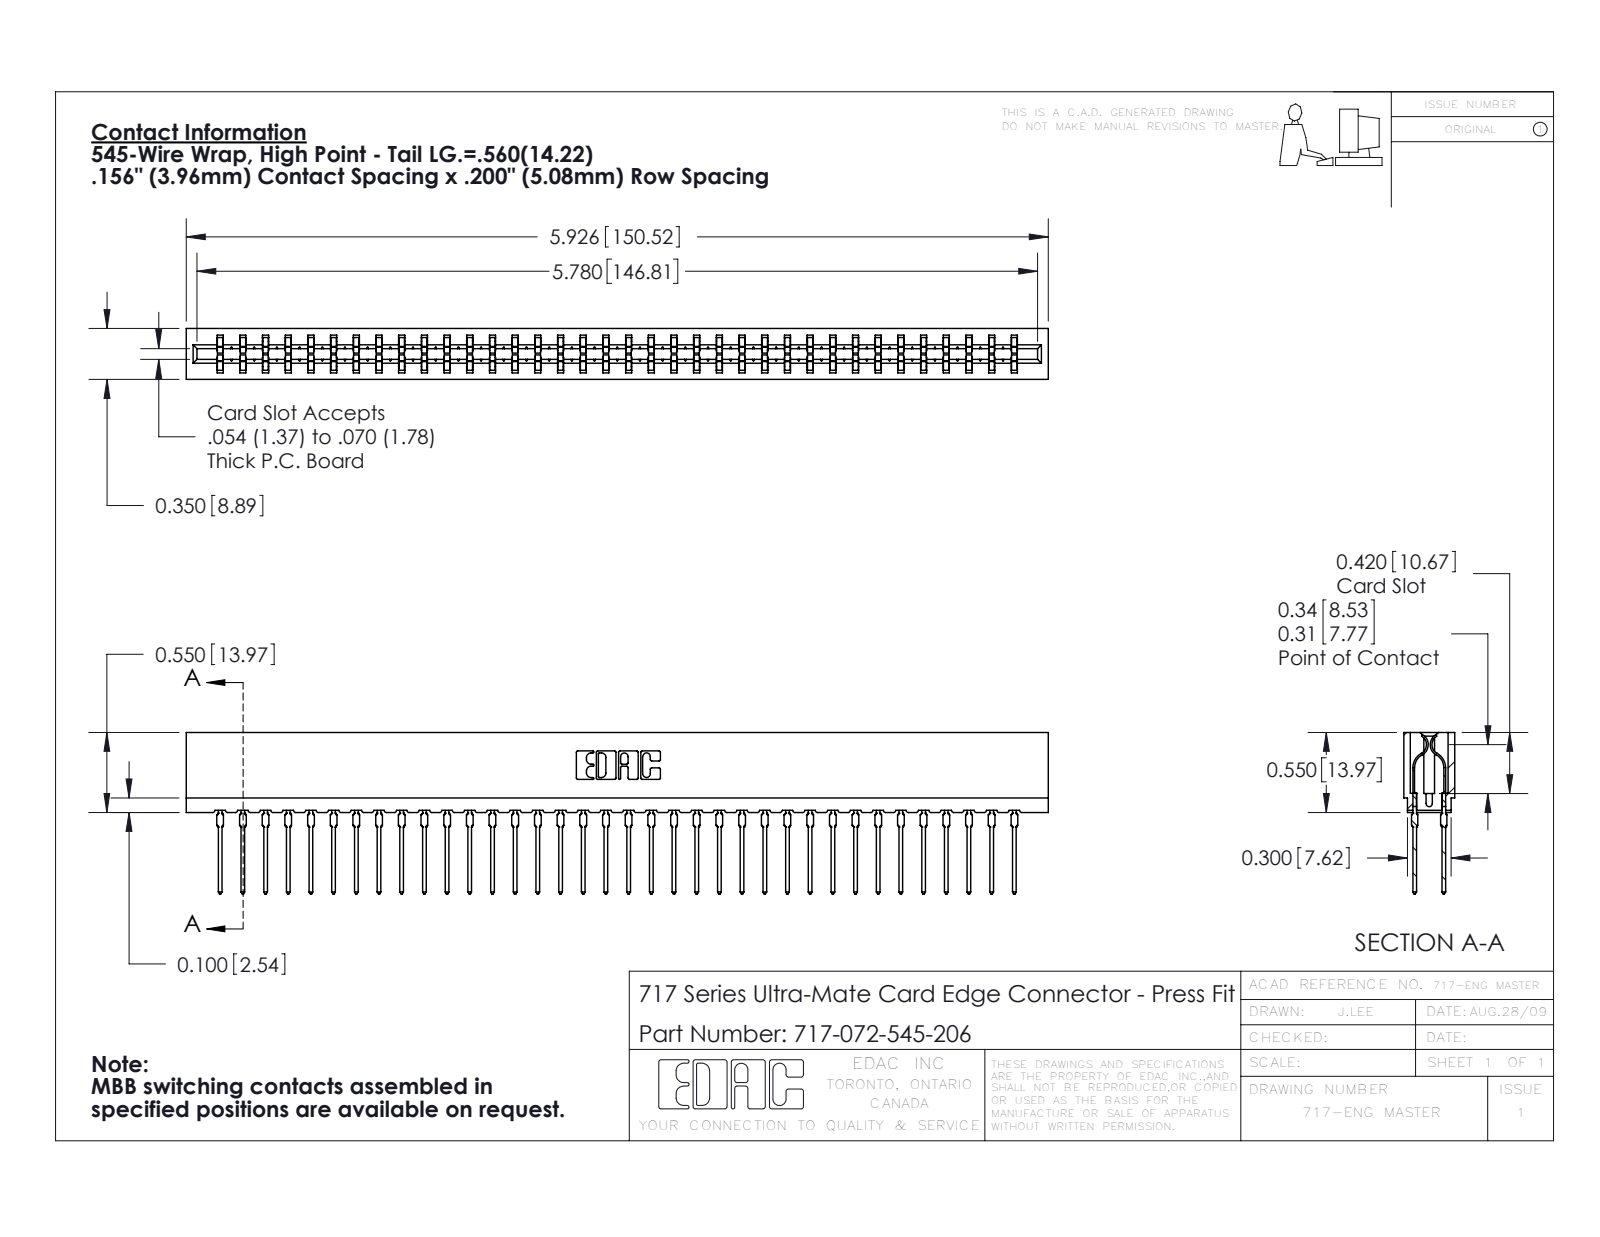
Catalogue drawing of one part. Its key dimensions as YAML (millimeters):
part_name: "745-292-001_545; 717-072-545-206; 717 Part_Insulator Option - 06"
step_written_by: "SolidWorks 2016 (CONFIG_CONTROL_DESIGN)"
units: millimeters
bodies: {solids: 73, faces: 6574, planar: 3402, cylindrical: 1300, other: 1872}
overall_size: [150.5, 28.2, 8.9]
volume: 13300
surface_area: 21520
partial_cylinders:
  - {radius: 0.5, count: 144}
  - {radius: 0.4, count: 72}
  - {radius: 0.3, count: 22}
  - {radius: 0.1, count: 8}
  - {radius: 0.3, count: 8}
  - {radius: 0.2, count: 6}
  - {radius: 0.8, count: 6}
  - {radius: 0.7, count: 3}
face_to_face_distances: [5.4, 3.5, 8.9, 1.6, 7.3, 1.9, 3.8, 1.9, 2.2, 6.7]
